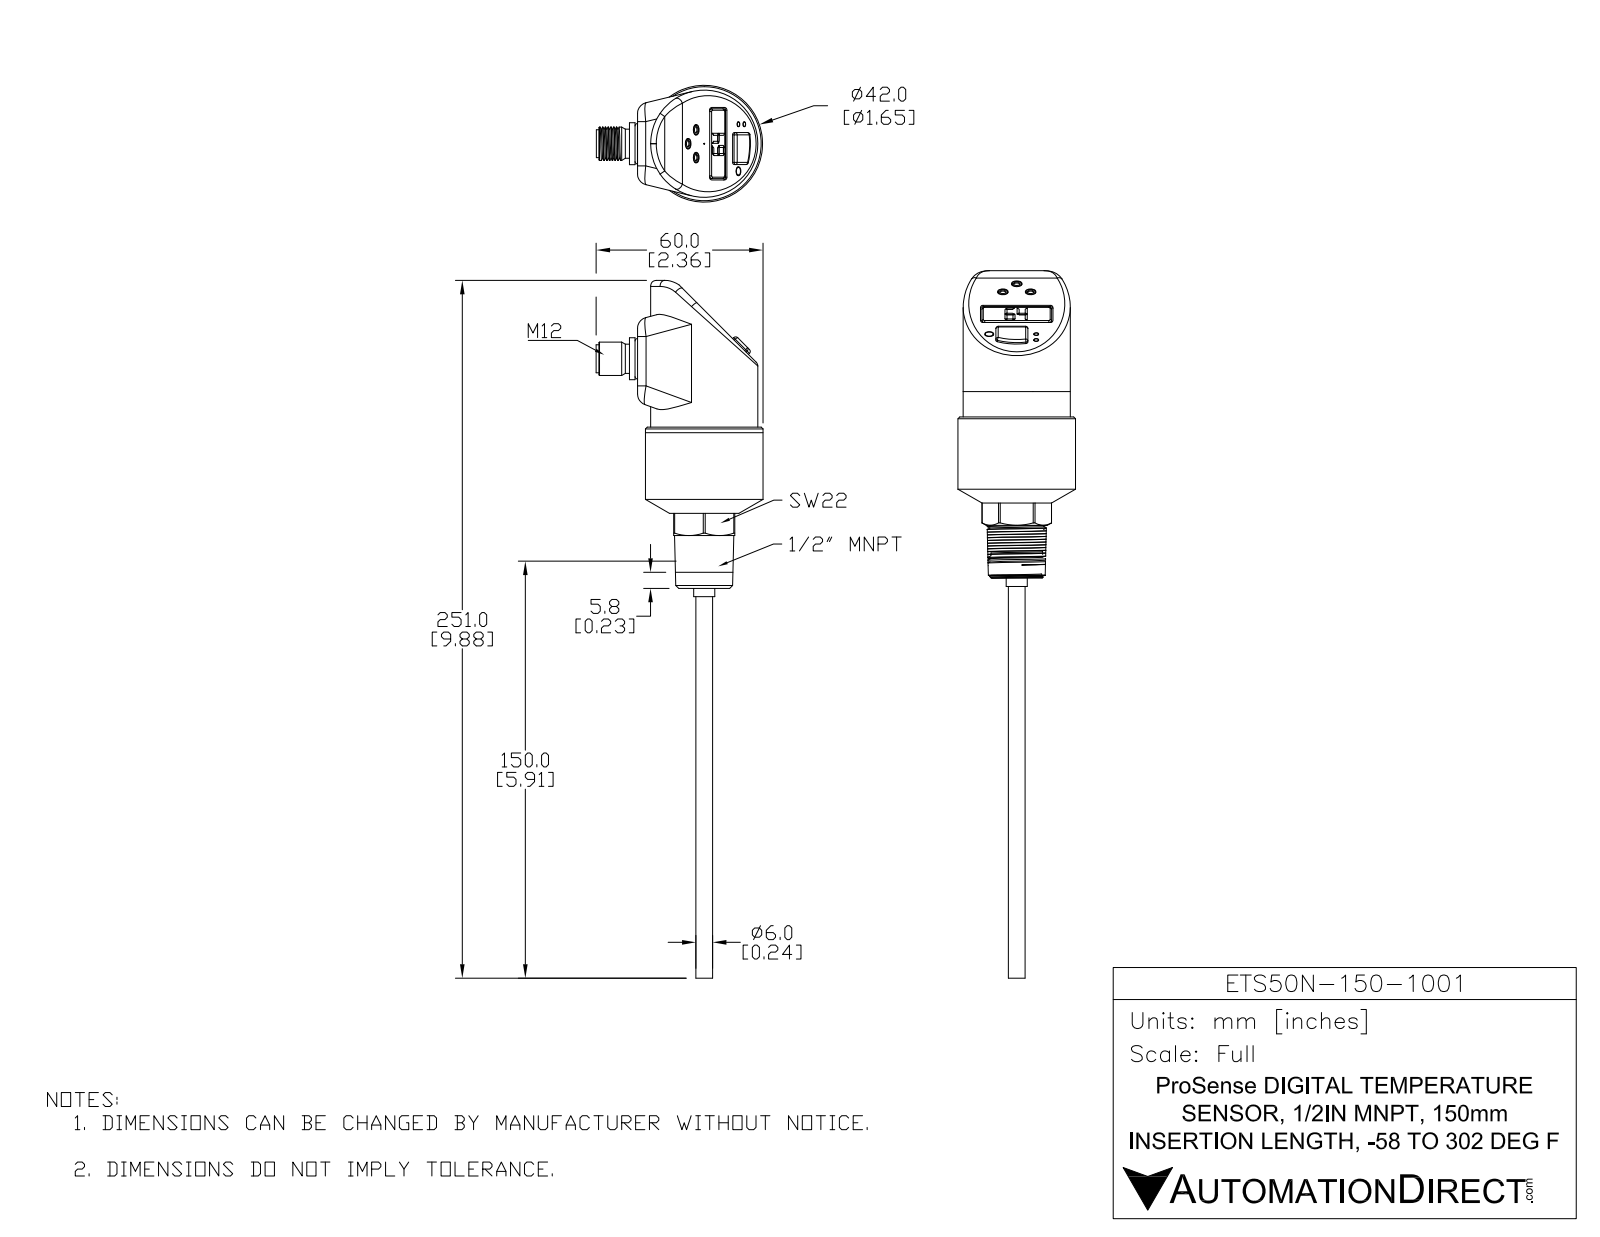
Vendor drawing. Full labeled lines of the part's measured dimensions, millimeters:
Part name (STEP PRODUCT): ETS50N-150-1001
STEP written by: SolidWorks 2016 (AUTOMOTIVE_DESIGN)
Units: millimetres
Bodies: 1 solid, 324 faces (138 planar, 95 cylindrical, 91 other)
Overall size (bounding box): 254.49 × 59.95 × 42.3
Volume: 110 571 mm³ · Surface area: 20 604 mm²
Round holes (diameter × count): ⌀8.45 ×1, ⌀11 ×1
Round bosses / shafts (diameter × count): ⌀1.4 ×4, ⌀1 ×4, ⌀42.3 ×1, ⌀38.55 ×1, ⌀15.1 ×1, ⌀14.56 ×1, ⌀12 ×1, ⌀10.5 ×1
Partial cylindrical surfaces — rounded edges, fillets, slot ends (radius × count): R1 ×8, R0.8 ×7, R0.5 ×4, R3.99 ×4, R7 ×4, R0.61 ×1, R2 ×1, R9.01 ×1
Main face-to-face distances: 22, 57.99, 13.9, 13, 0.9, 2, 2.9, 15.9, 37.9, 35
